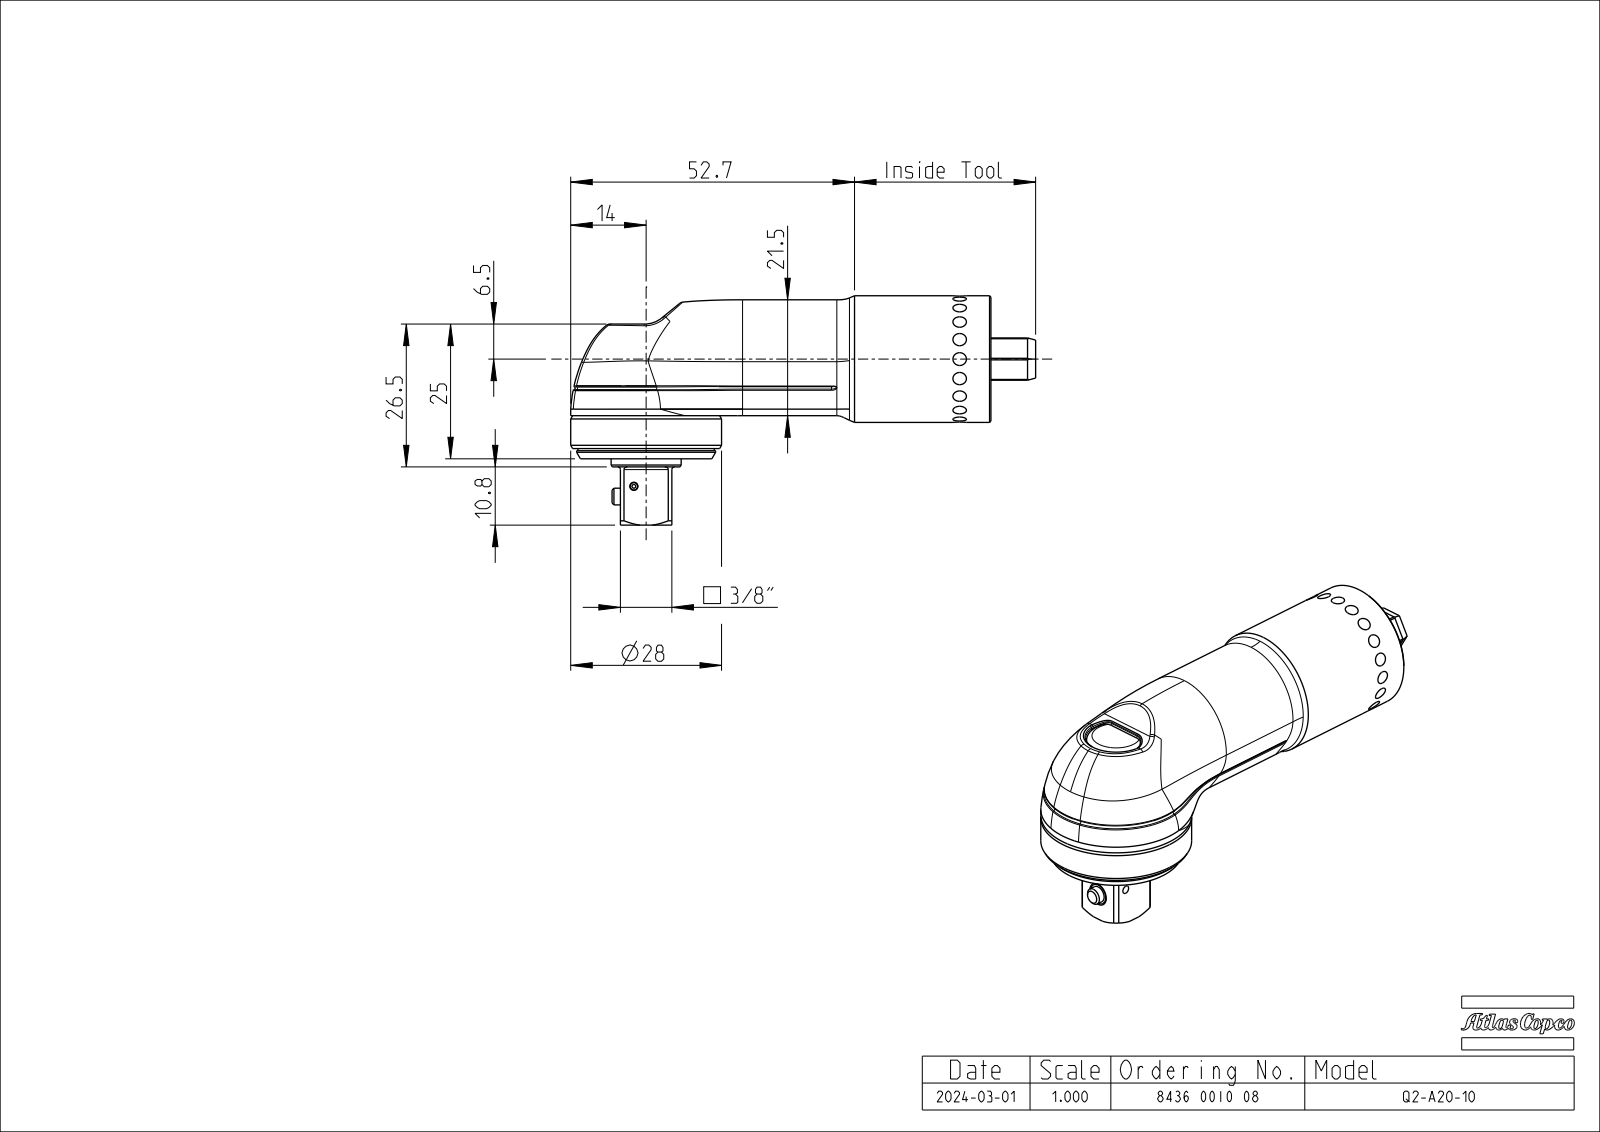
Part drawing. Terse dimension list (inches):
name: 4211580780_NOIP
written by: CREO PARAMETRIC BY PTC INC, 2022414 (CONFIG_CONTROL_DESIGN)
unit: in
bodies: 1 solid, 202 faces (24 planar, 42 cylindrical, 136 other)
size: 3.071 × 1.675 × 1.102
volume: 2.176 in³; area: 11.63 in²
holes: 4× ⌀0.11, 1× ⌀0.049
bosses: 1× ⌀1.102, 1× ⌀1.016, 1× ⌀0.996, 1× ⌀0.925, 1× ⌀0.512, 1× ⌀0.122
rounds: 4× R0.008, 4× R0.02, 2× R0.012, 1× R0.016, 1× R0.197, 1× R0.248, 1× R0.433, 1× R0.669
face distances: 0.376, 2.331, 0.075, 2.708, 0.975, 0.9, 0.484, 0.559, 1.459, 0.799
hole spacings: 0.384, 0.543, 0.768
